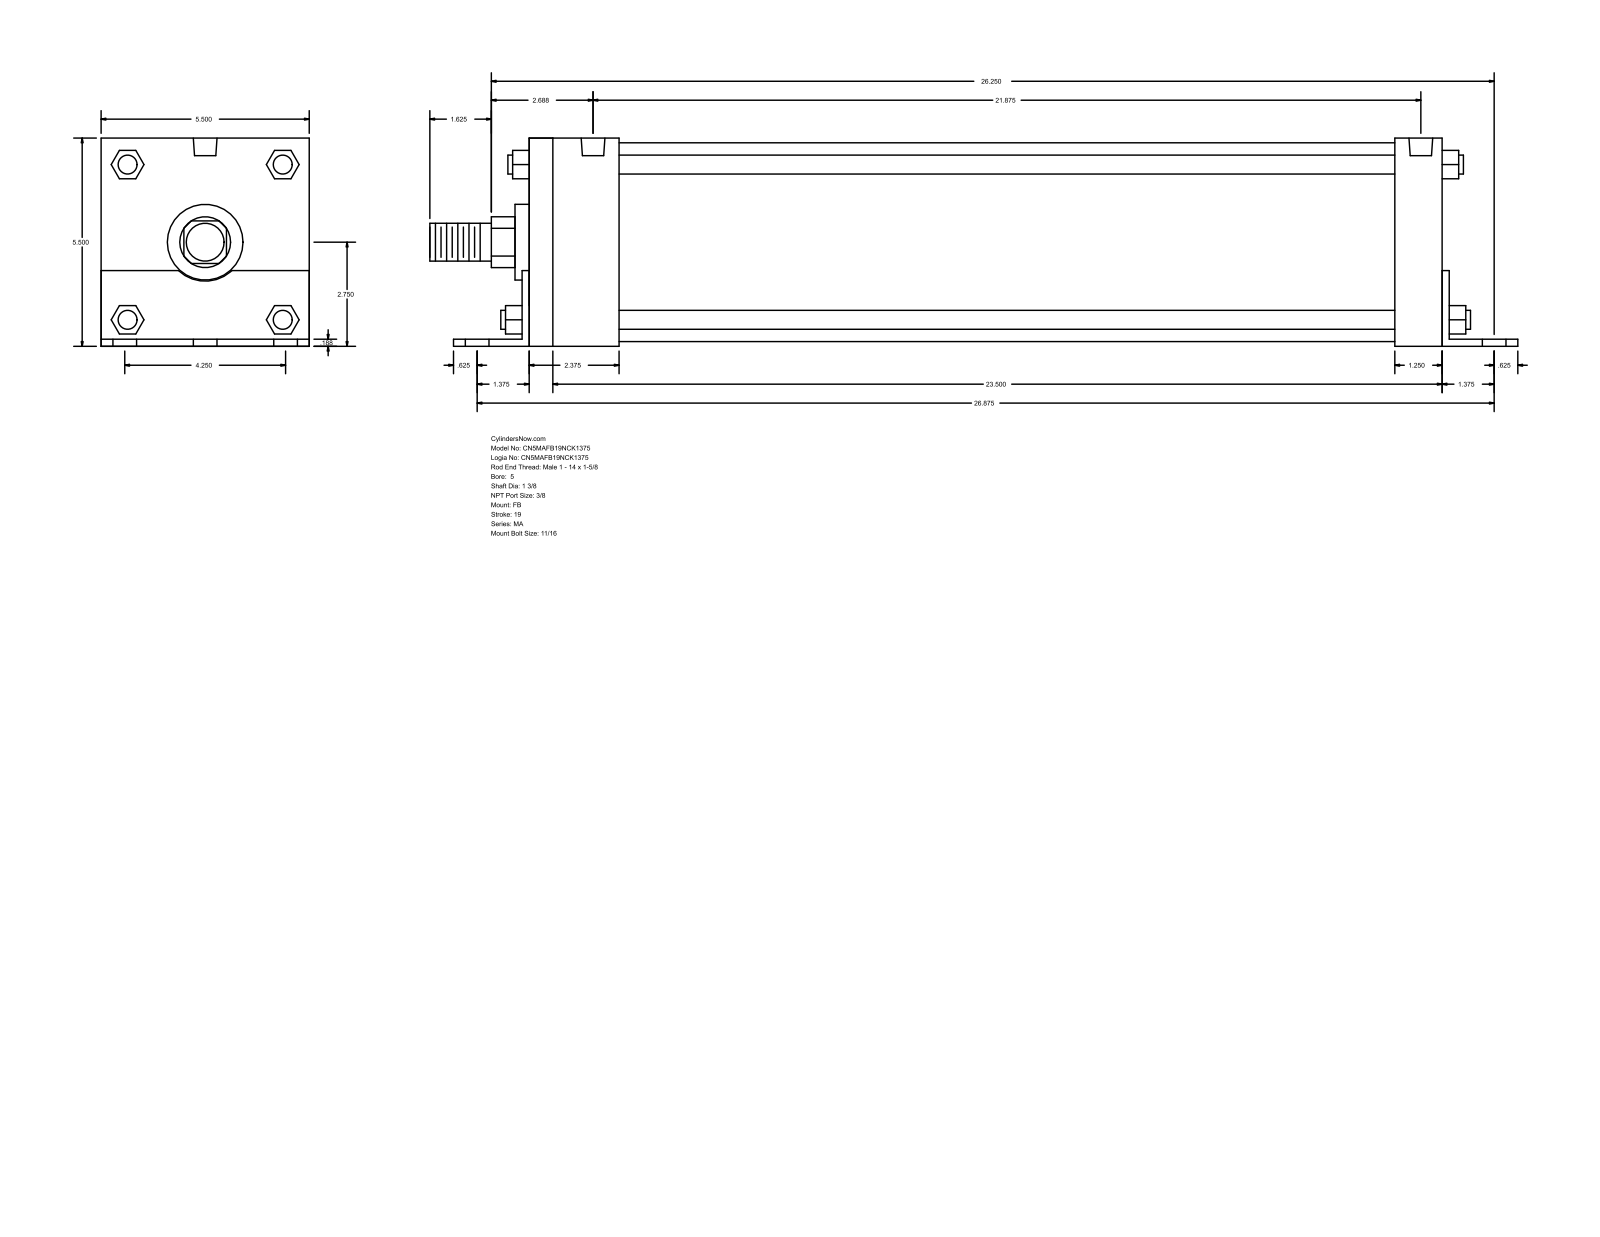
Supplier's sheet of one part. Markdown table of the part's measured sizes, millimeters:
| quantity | value |
| --- | --- |
| part name | MA_FB__0500_1.375 |
| STEP written by | GSSL Pune (CONFIG_CONTROL_DESIGN) |
| units | millimeters |
| bodies | 0 solids, 140 faces (105 planar, 35 cylindrical, 0 other) |
| overall size | 730.25 × 139.75 × 139.7 |
| round holes (diameter × count) | 17.46 × 6, 11.11 × 4, 15.93 × 2 |
| round bosses / shafts (diameter × count) | 12.7 × 4, 133.35 × 1, 50.8 × 1, 34.92 × 1, 25.4 × 1 |
| partial cylindrical surfaces (radius × count) | 17.06 × 1, 26.16 × 1 |
| main face-to-face distances | 139.7, 4.76, 139.75, 4.71, 134.99, 612.77, 4.77, 617.54, 617.53, 622.3 |
| hole center spacings | 53.98, 684.76, 682.63, 4.77, 73.04, 76.34, 94.68, 98.64 |
